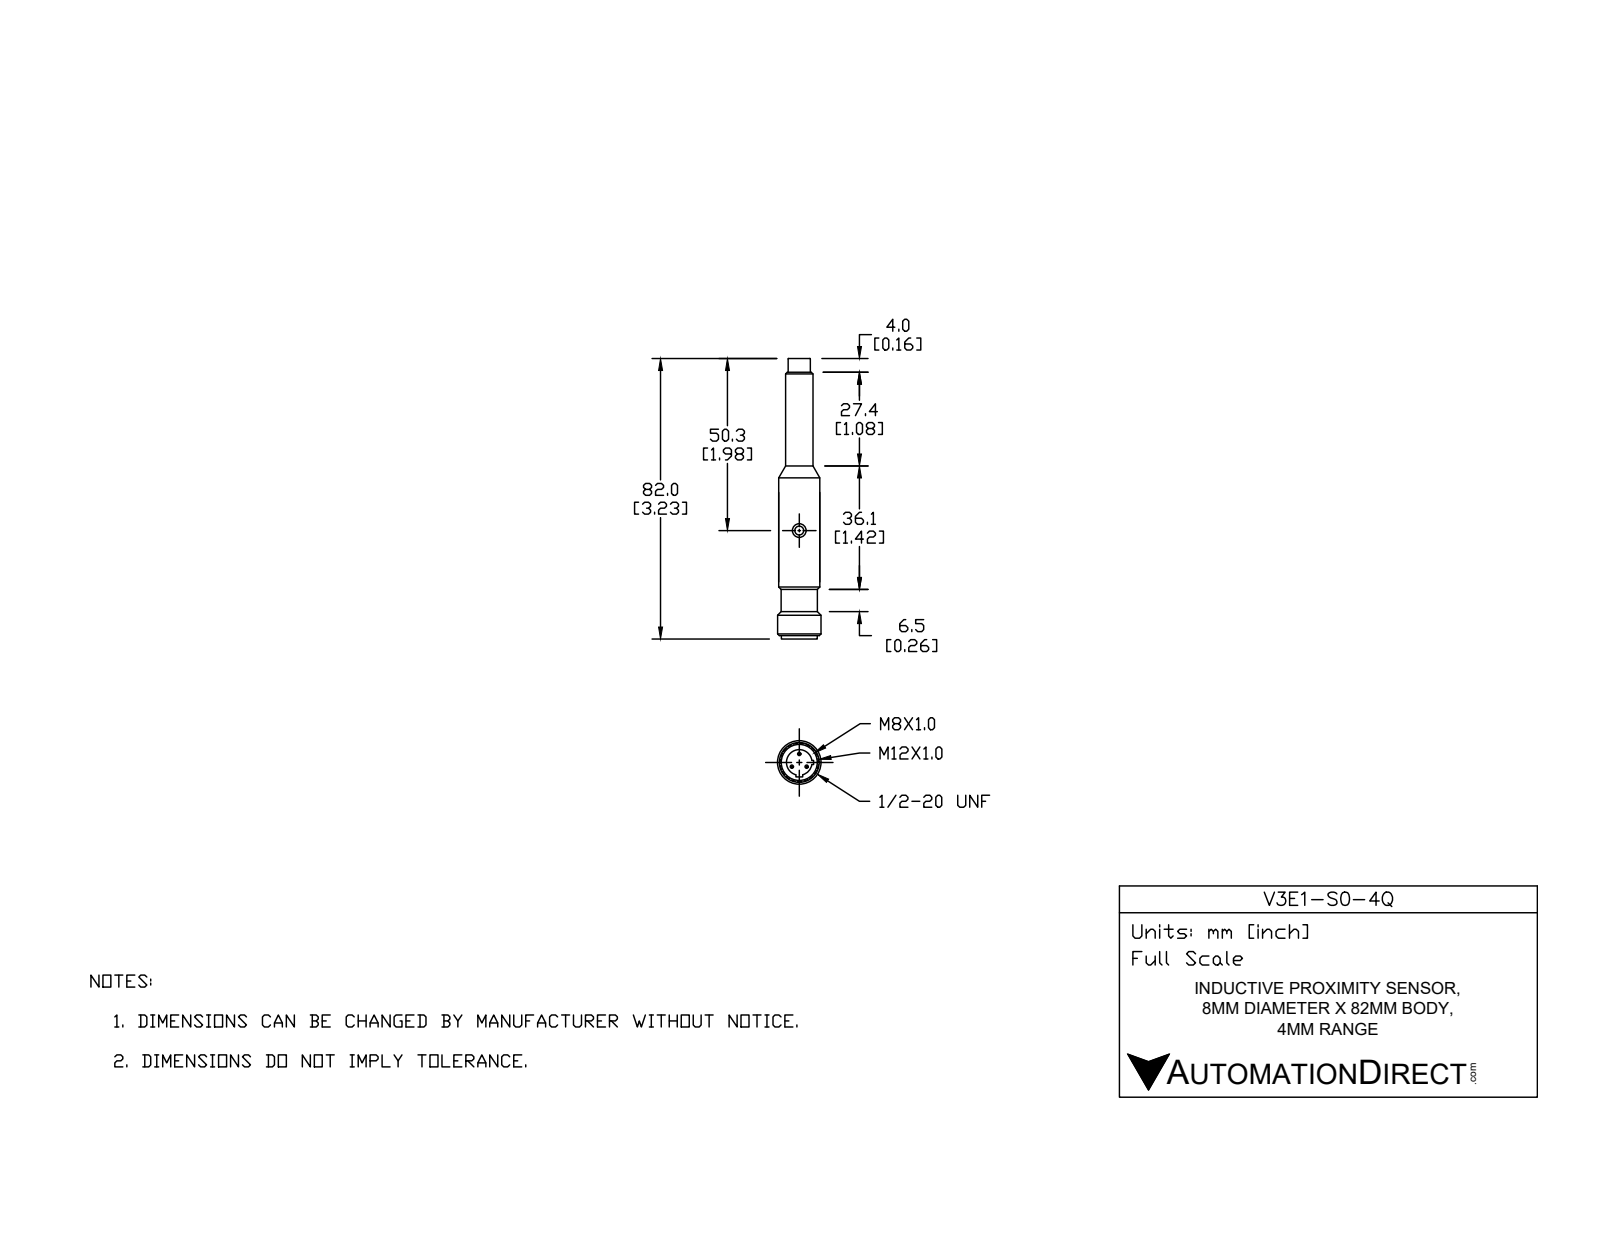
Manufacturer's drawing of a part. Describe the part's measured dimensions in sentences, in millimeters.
The part is named "V3E1_4Q_fig". Its 3-D file was written by "ST-DEVELOPER v16.7 (AUTOMOTIVE_DESIGN)". It is 1 solid with 45 faces: 19 planar, 16 cylindrical and 10 other. Overall it measures 82 by 12.7 by 12.7 millimeters. Its volume is 6 667 cubic millimeters and its surface area 3 324 square millimeters. Round holes: 1 of diameter 2.6, 1 of diameter 4, 1 of diameter 7.5, 1 of diameter 9.5. Round bosses or shafts: 3 of diameter 0.98, 1 of diameter 12.7, 1 of diameter 12, 1 of diameter 10.6, 1 of diameter 10.5, 1 of diameter 9.55, 1 of diameter 9.4, 1 of diameter 8. The main face-to-face distances are 6.8, 75.2, 82, 1, 81, 5.8, 9.5, 8.7, 0.8, 4.
